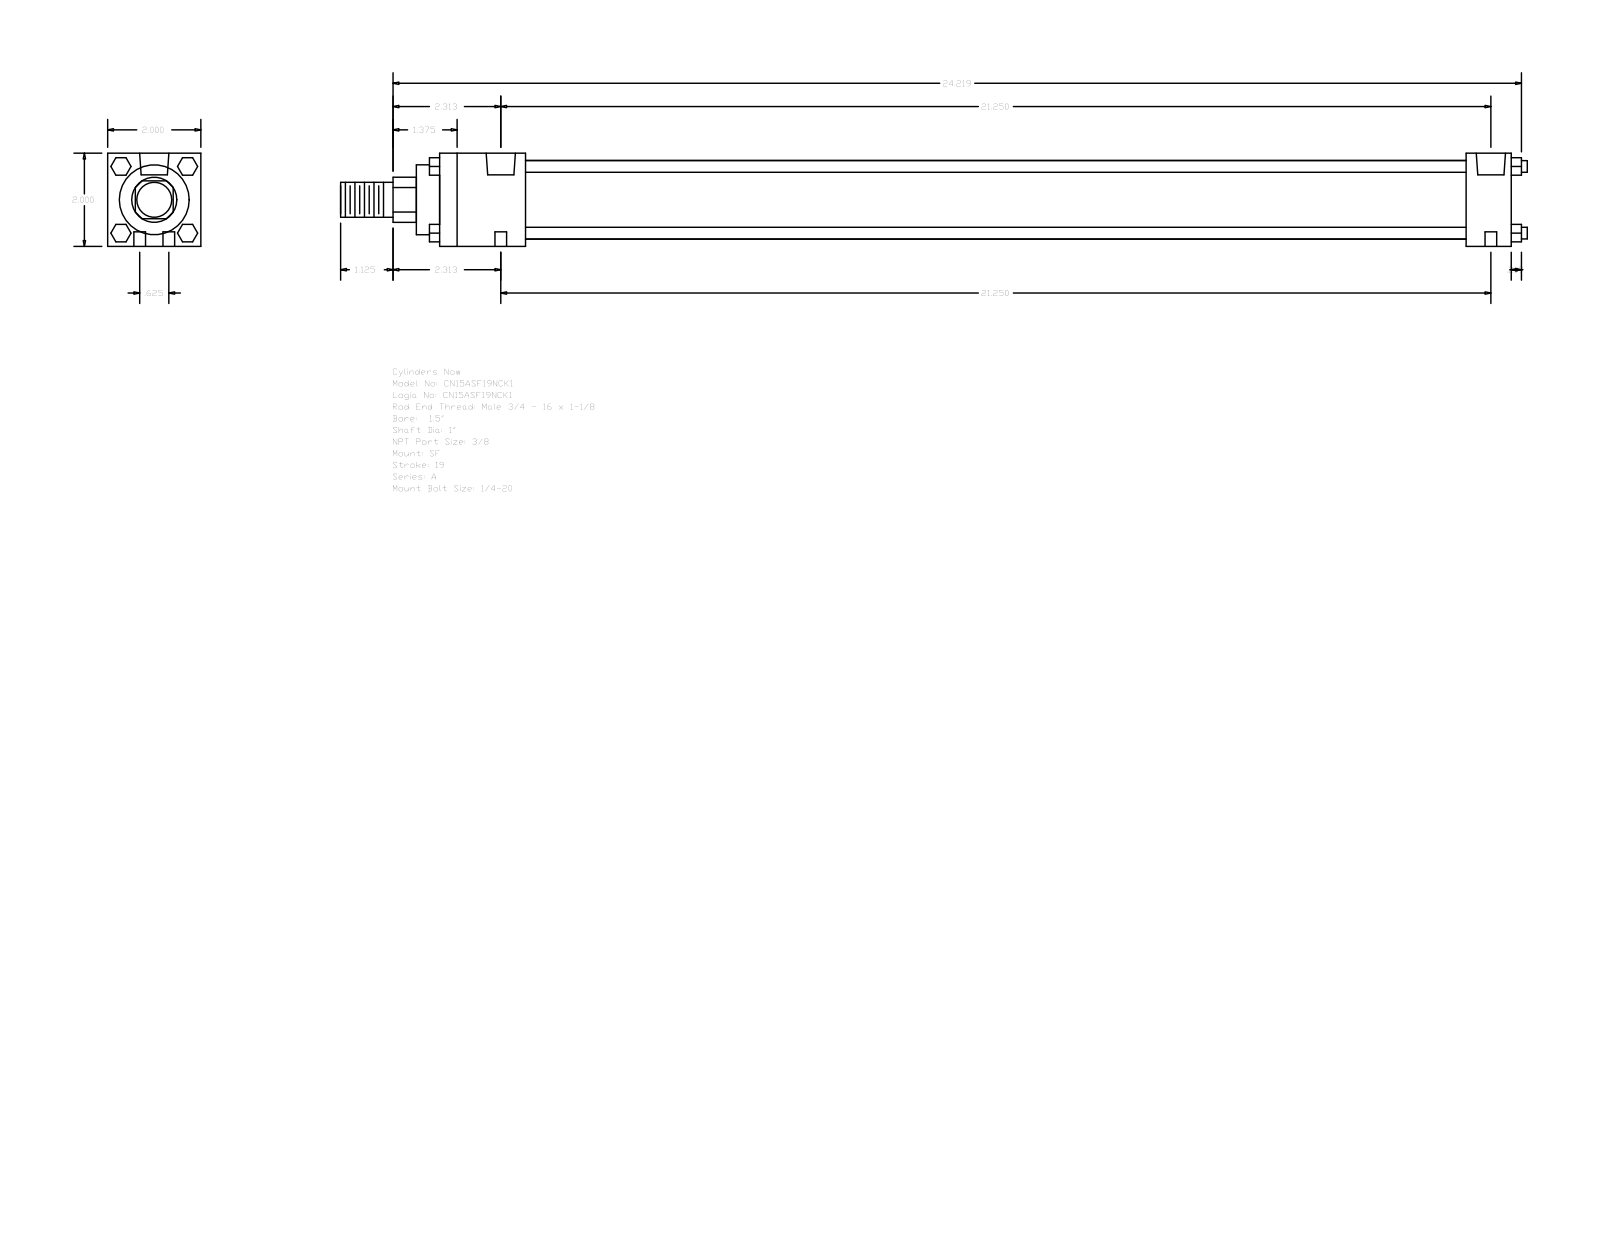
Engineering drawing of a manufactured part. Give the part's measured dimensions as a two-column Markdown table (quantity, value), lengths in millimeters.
| quantity | value |
| --- | --- |
| part name | A_SF__0150_1 |
| STEP written by | GSSL Pune (CONFIG_CONTROL_DESIGN) |
| units | millimeters |
| bodies | 0 solids, 124 faces (94 planar, 30 cylindrical, 0 other) |
| overall size | 646.91 × 50.8 × 50.8 |
| round holes (diameter × count) | 6.35 × 4, 5.56 × 2, 15.93 × 2 |
| round bosses / shafts (diameter × count) | 6.35 × 4, 42.93 × 1, 38.1 × 1, 25.4 × 1, 19.05 × 1 |
| partial cylindrical surfaces (radius × count) | 12.29 × 1 |
| main face-to-face distances | 50.8, 584.2, 46.83, 559.59, 512.76, 537.37, 24.61, 12.7, 59.53, 572.29 |
| hole center spacings | 7.94, 539.81, 539.75, 15.88, 539.98, 531.81 |
